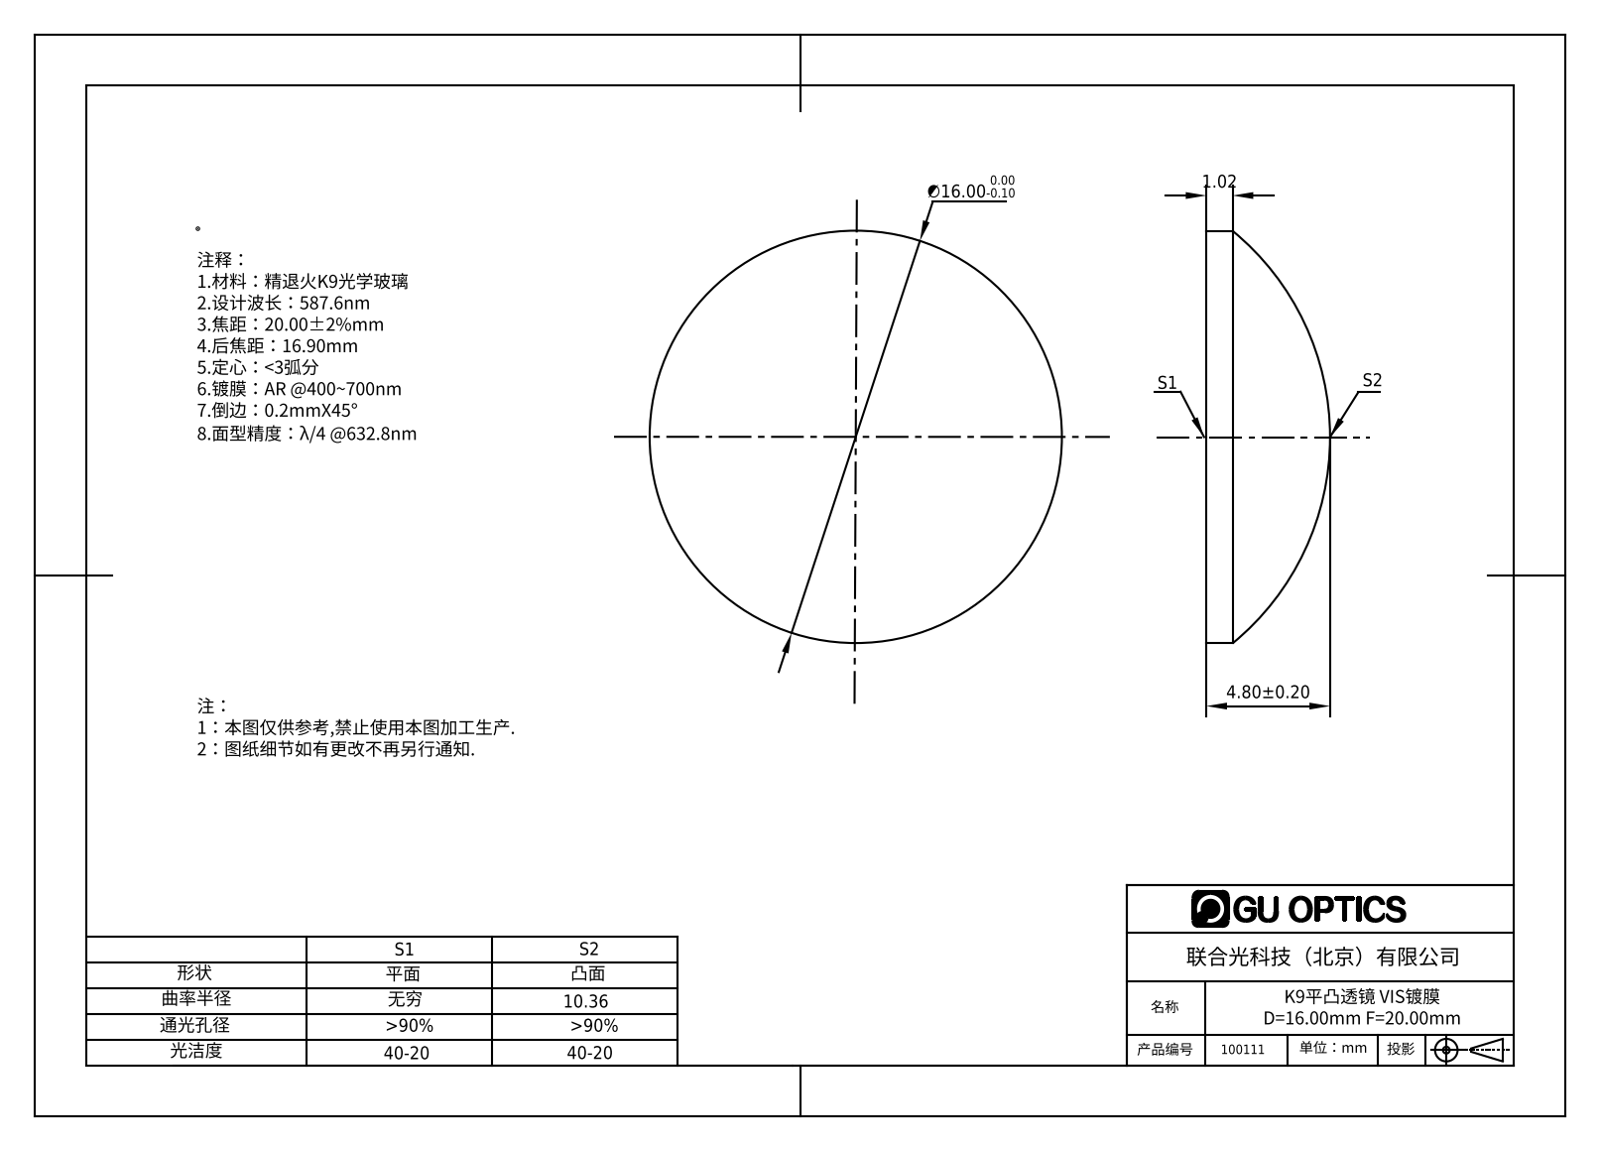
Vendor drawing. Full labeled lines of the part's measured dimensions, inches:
Part name (STEP PRODUCT): 100283
STEP written by: SolidWorks 2016 (AUTOMOTIVE_DESIGN)
Units: inches
Bodies: 1 solid, 5 faces (1 planar, 2 cylindrical, 2 other)
Overall size (bounding box): 0.63 × 0.63 × 0.189
Volume: 0.037 in³ · Surface area: 0.772 in²
Round bosses / shafts (diameter × count): ⌀0.63 ×1
